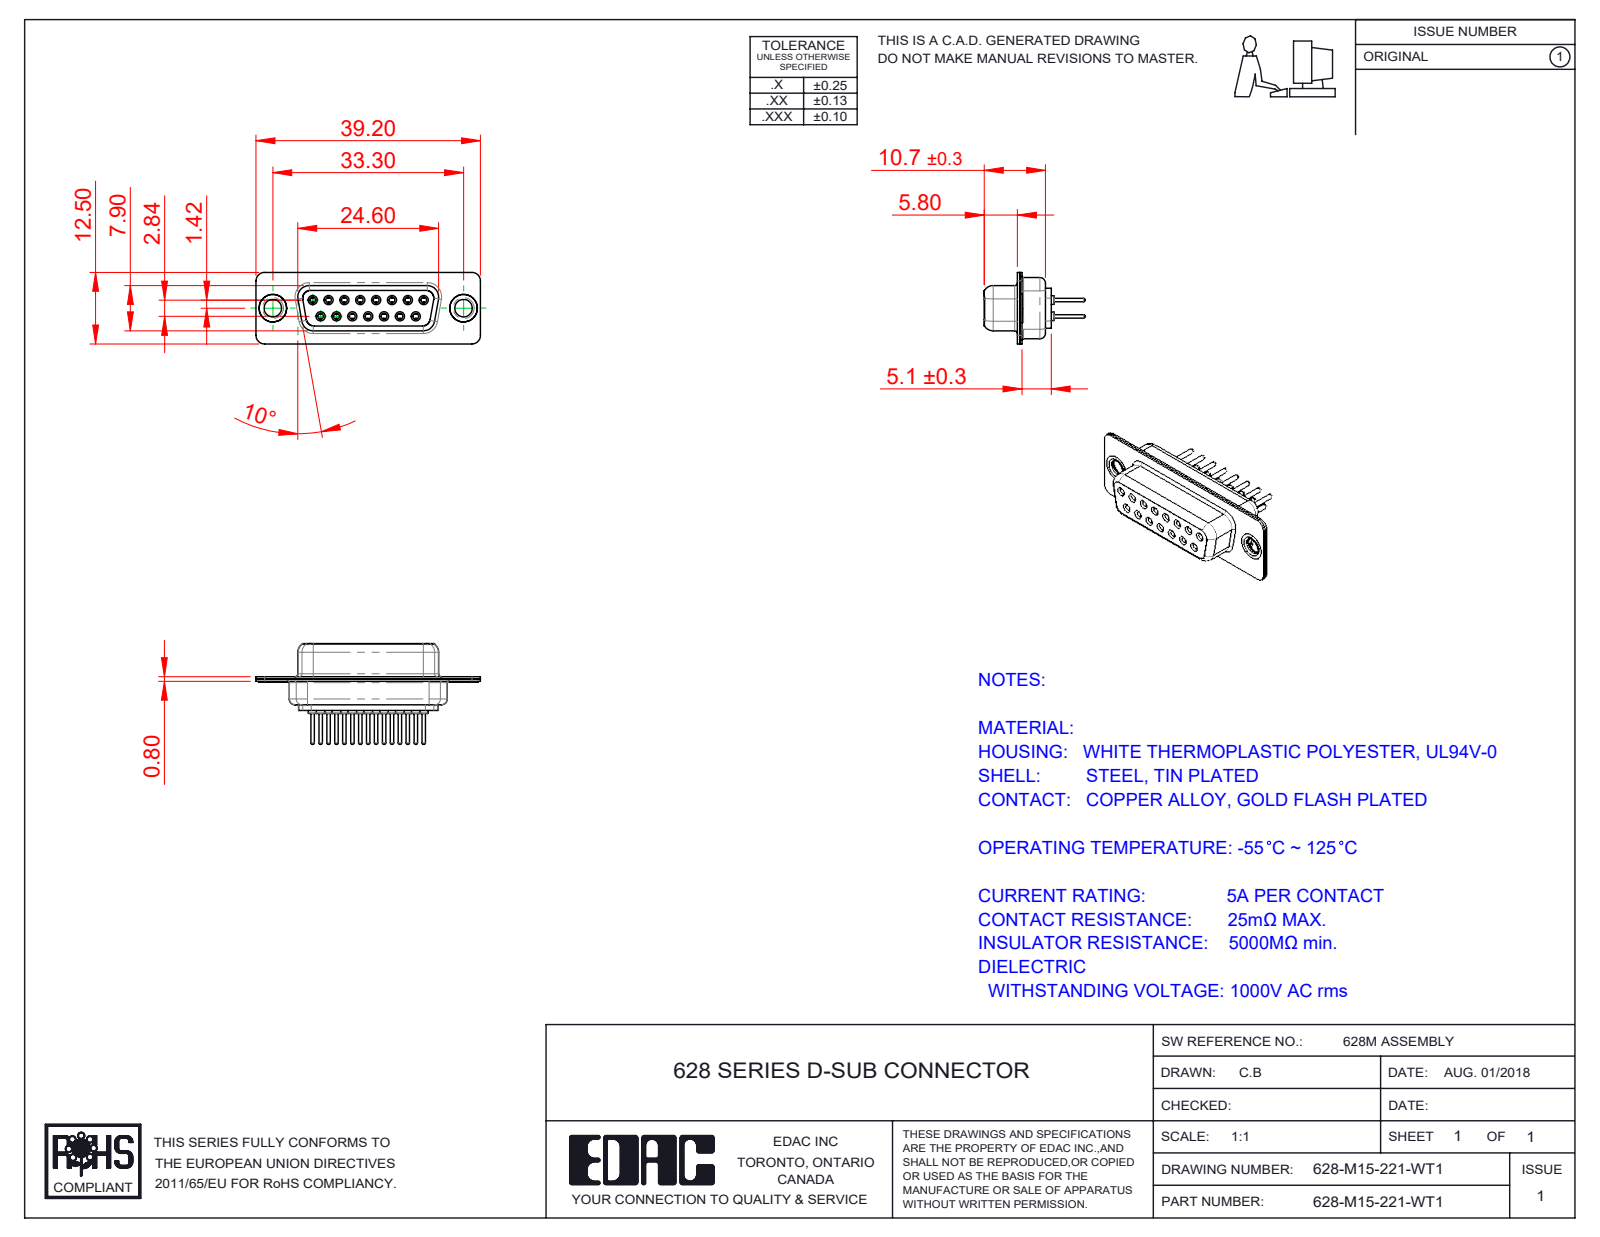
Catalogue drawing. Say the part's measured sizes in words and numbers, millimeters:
The part is named "628M Shell Rear_15 Contacts; 628M Housing_15 Contacts; 628M Contact Row 2_21; 628M Shell Front_15 Contacts (+3 more)". Its 3-D file was written by "SolidWorks 2020 (CONFIG_CONTROL_DESIGN)". It is 20 solids with 1078 faces: 292 planar, 406 cylindrical and 380 other. Overall it measures 39.2 by 17.6 by 12.5 millimeters. Its volume is 2 393 cubic millimeters and its surface area 6 054 square millimeters. Round holes: 15 of diameter 1, 15 of diameter 1.1, 15 of diameter 1.7, 15 of diameter 1.8, 15 of diameter 2, 2 of diameter 3.05, 2 of diameter 4, 2 of diameter 4.8. Round bosses or shafts: 15 of diameter 2.2, 15 of diameter 1.6, 15 of diameter 1.5, 15 of diameter 0.6, 2 of diameter 5, 2 of diameter 4.9, 2 of diameter 3.55. Partial cylindrical surfaces (rounded edges, fillets, slot ends): 16 of radius 1.5, 12 of radius 2, 8 of radius 1.35, 8 of radius 1.6, 4 of radius 0.25, 4 of radius 0.5, 4 of radius 0.6, 4 of radius 0.65. The main face-to-face distances are 0.4, 1.4, 0.45, 8.45, 8.9, 1.8, 6.2, 7.05, 1, 1.35. The hole center spacings are 3.16, 2.77, 5.54, 8.31, 11.08, 5.03, 5.04, 7.48.
